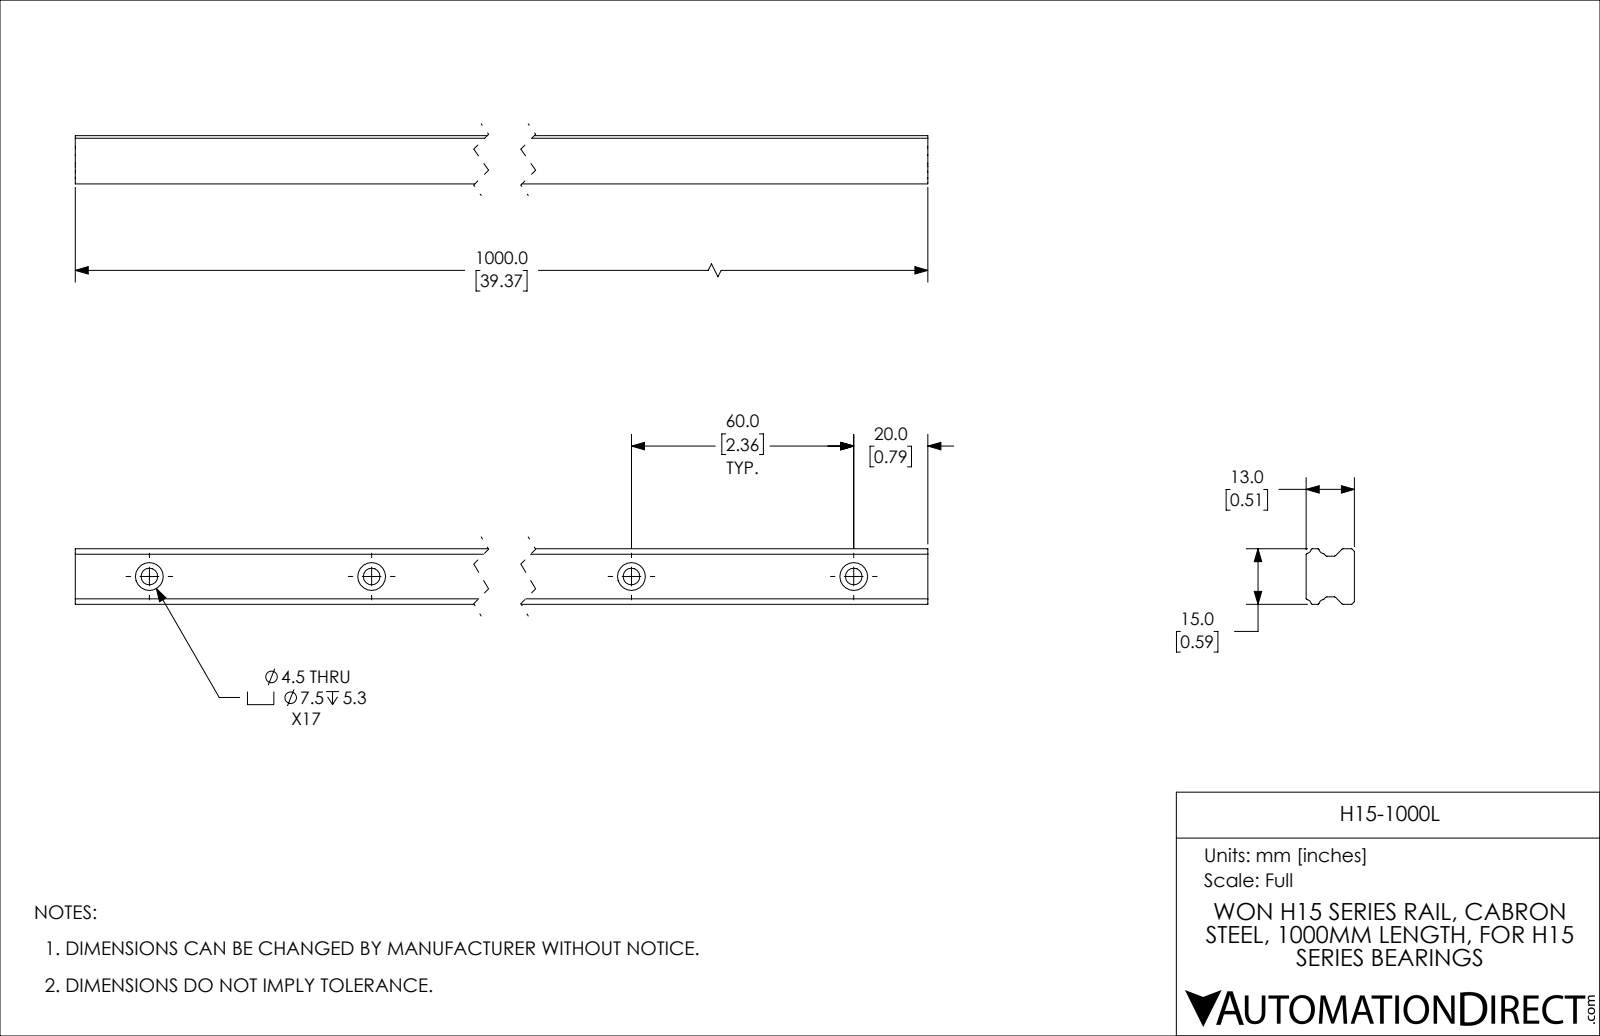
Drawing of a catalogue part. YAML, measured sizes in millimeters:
part_name: "H15-1000L"
step_written_by: "SolidWorks 2019 (CONFIG_CONTROL_DESIGN)"
units: millimeters
bodies: {solids: 1, faces: 119, planar: 33, cylindrical: 86, other: 0}
overall_size: [1000, 15, 13]
volume: 167189
surface_area: 60675
round_holes:
  - {diameter: 4.5, count: 17}
  - {diameter: 7.5, count: 17}
partial_cylinders:
  - {radius: 0.3, count: 6}
  - {radius: 0.5, count: 6}
  - {radius: 1.4, count: 4}
  - {radius: 0.6, count: 2}
face_to_face_distances: [13, 2, 15, 11, 12.37, 6.08, 6.29, 7.7, 5.3, 1000]
hole_center_spacings: [60, 120, 180, 240, 300, 360, 420, 480]
